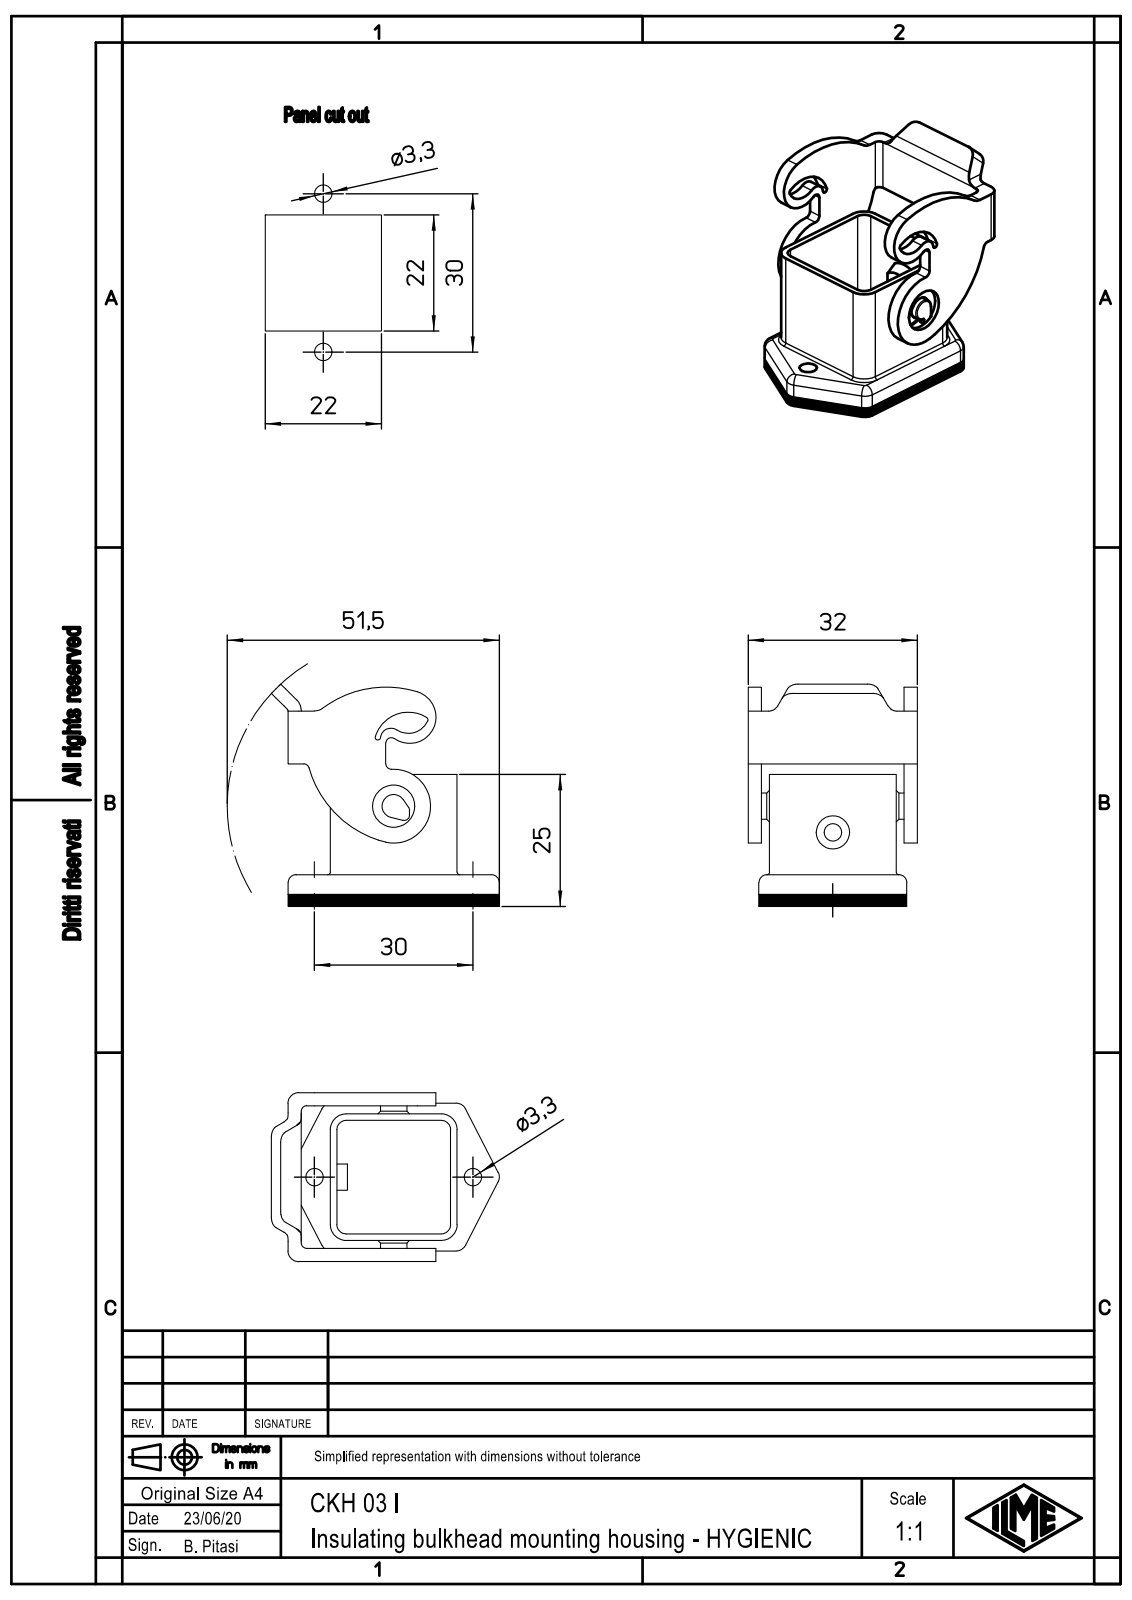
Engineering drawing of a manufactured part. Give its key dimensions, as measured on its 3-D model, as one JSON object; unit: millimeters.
{"part_name": "CKH 03 I", "step_written_by": "Creo Elements/Direct Modeling 20.1B 02-Apr-2019 (C) Parametric Technology GmbH (AUTOMOTIVE_DESIGN)", "units": "millimeters", "bodies": {"solids": 1, "faces": 265, "planar": 105, "cylindrical": 131, "other": 29}, "overall_size": [43.15, 42.13, 32], "volume_mm3": 8418, "surface_area_mm2": 9272, "round_holes": [[3.3, 3], [4.2, 1], [8, 1]], "round_bosses_or_shafts": [[5, 1], [4, 1]], "partial_cylinders_radius": [[0.25, 14], [2, 13], [0.2, 8], [0.5, 7], [1, 7], [1.5, 6], [3, 6], [1.75, 4]], "face_to_face_distances": [2.5, 1.25, 22.75, 29.5, 26.75, 2.75, 5.25, 24.25, 21.5, 32], "hole_center_spacings": [30]}
